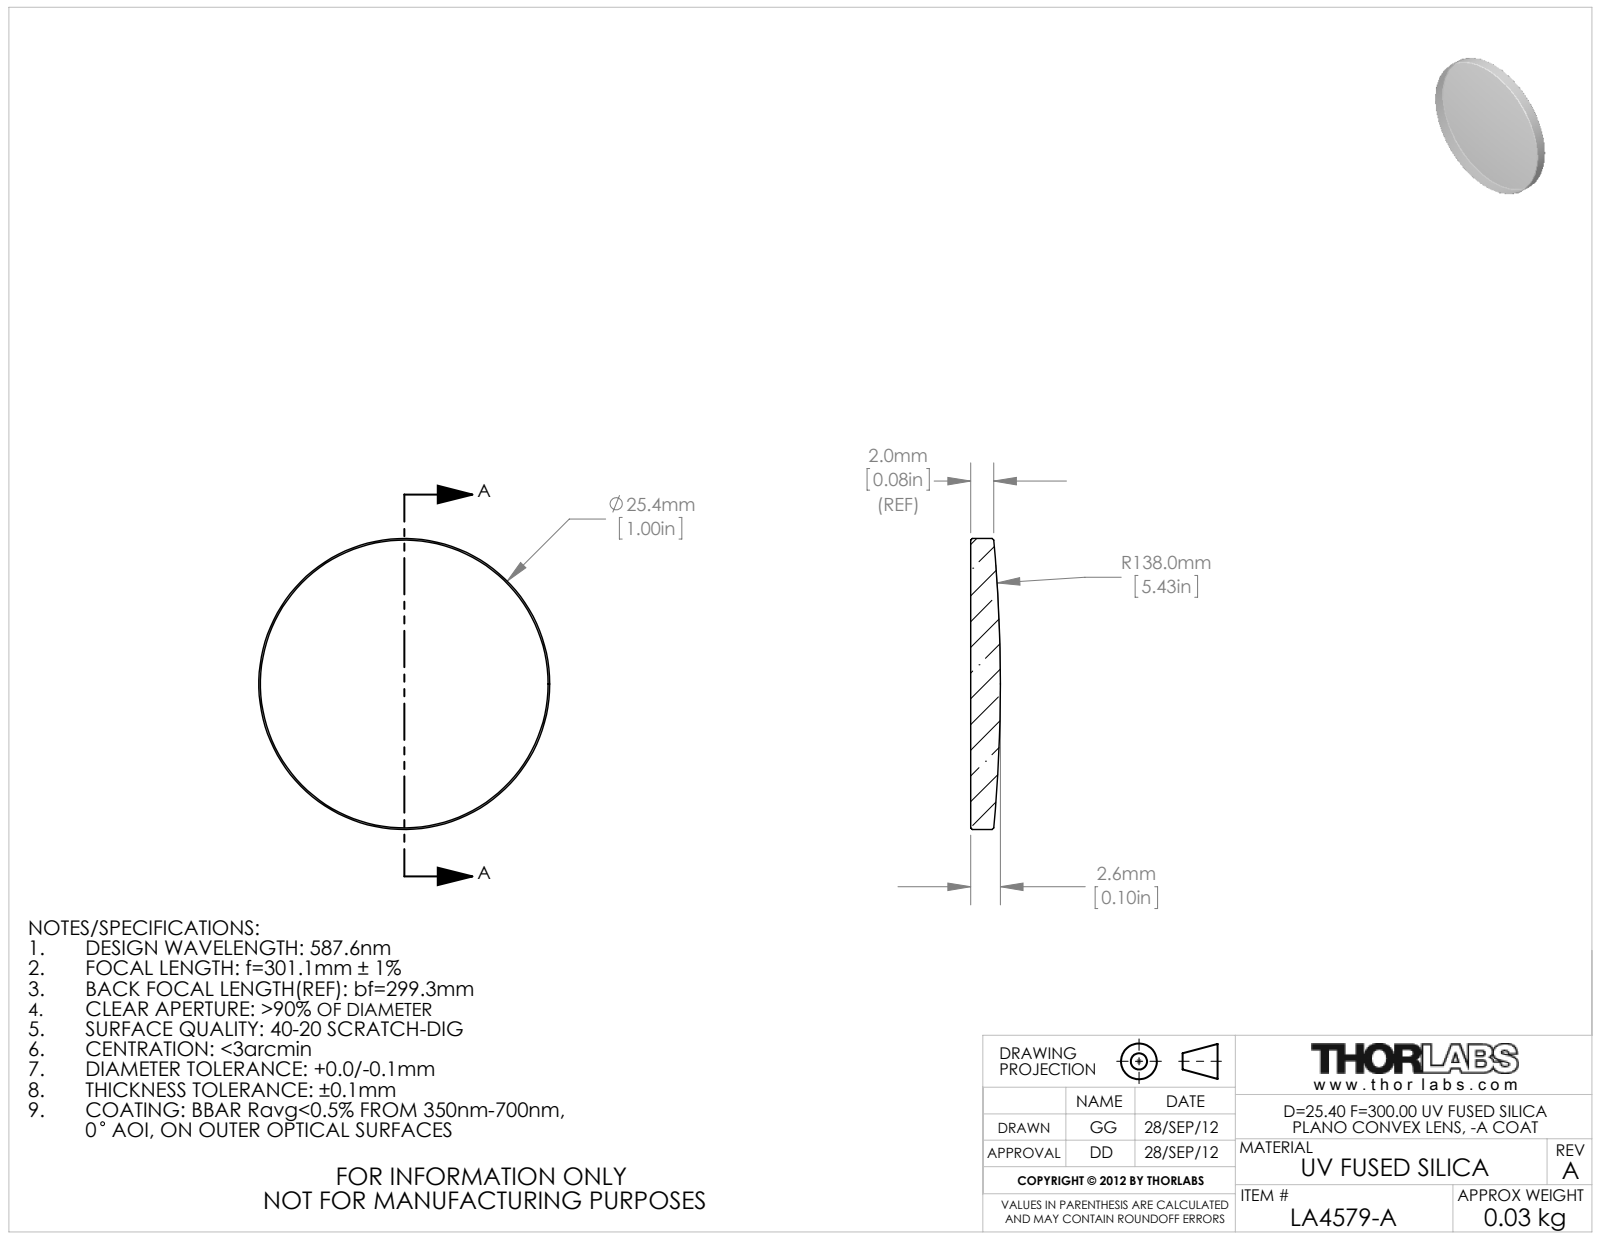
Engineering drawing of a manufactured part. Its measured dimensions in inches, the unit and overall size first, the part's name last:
Units: inches
Overall size (bounding box): 1 × 1 × 0.102
Round bosses / shafts (diameter × count): ⌀1 ×1
Volume: 0.071 in³ · Surface area: 1.801 in²
Bodies: 1 solid, 9 faces (1 planar, 2 cylindrical, 6 other)
Part name (STEP PRODUCT): 24993-E0W
STEP written by: SolidWorks 2011 (CONFIG_CONTROL_DESIGN)
